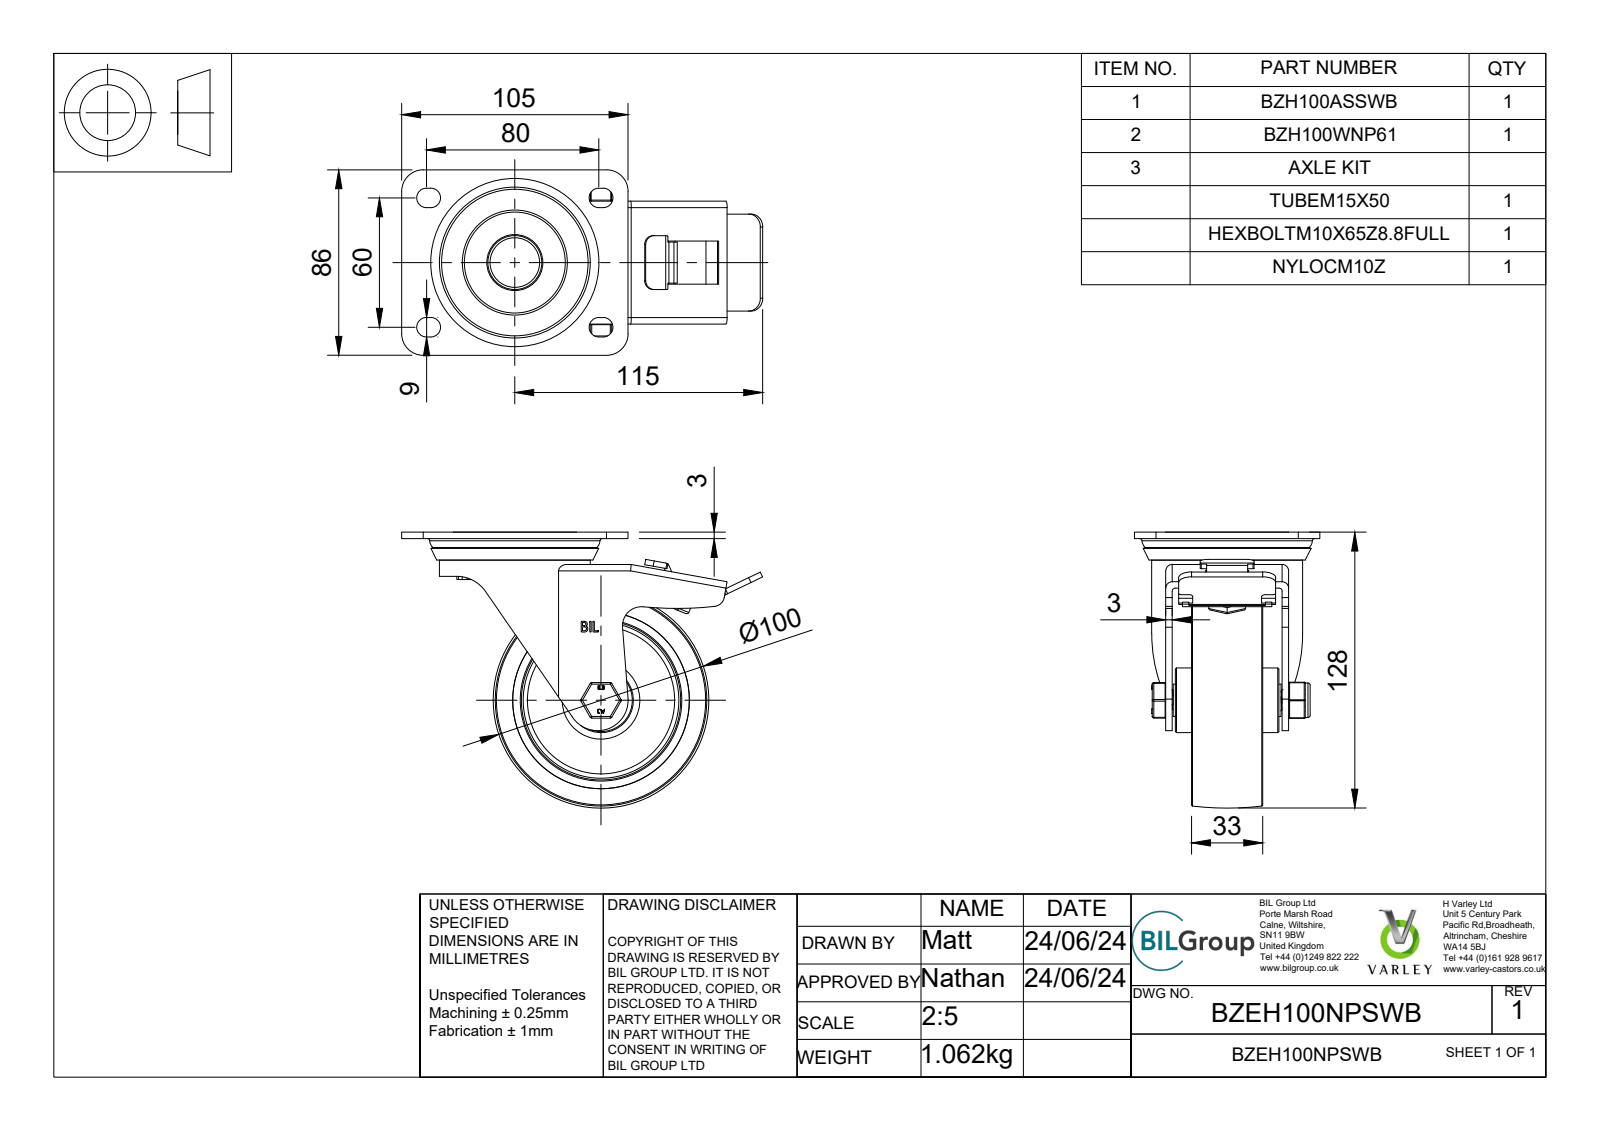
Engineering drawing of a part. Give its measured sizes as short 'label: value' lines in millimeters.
name: BZEH100NPSWB v4; BZH100WNP61 v1; POLYURETHANE TYRE; NYLON RIM (+8 more)
written by: Autodesk Translation Framework v13.14.0.145 (AUTOMOTIVE_DESIGN)
unit: mm
bodies: 32 solids, 658 faces (311 planar, 201 cylindrical, 146 other)
size: 167.5 × 128 × 86
volume: 279 825 mm³; area: 140 694 mm²
holes: 1× ⌀8, 1× ⌀10, 1× ⌀10.2, 1× ⌀10.5, 1× ⌀12, 1× ⌀15.4, 1× ⌀30, 1× ⌀64, 1× ⌀82
bosses: 1× ⌀70, 1× ⌀54, 1× ⌀30, 1× ⌀25, 1× ⌀21, 1× ⌀16, 1× ⌀15, 1× ⌀9.85
rounds: 20× R0.5, 12× R0.75, 9× R4.5, 8× R1, 6× R1.5, 4× R3, 4× R10, 3× R2
face distances: 3, 5, 12, 9, 14, 19, 10, 2, 45, 1
